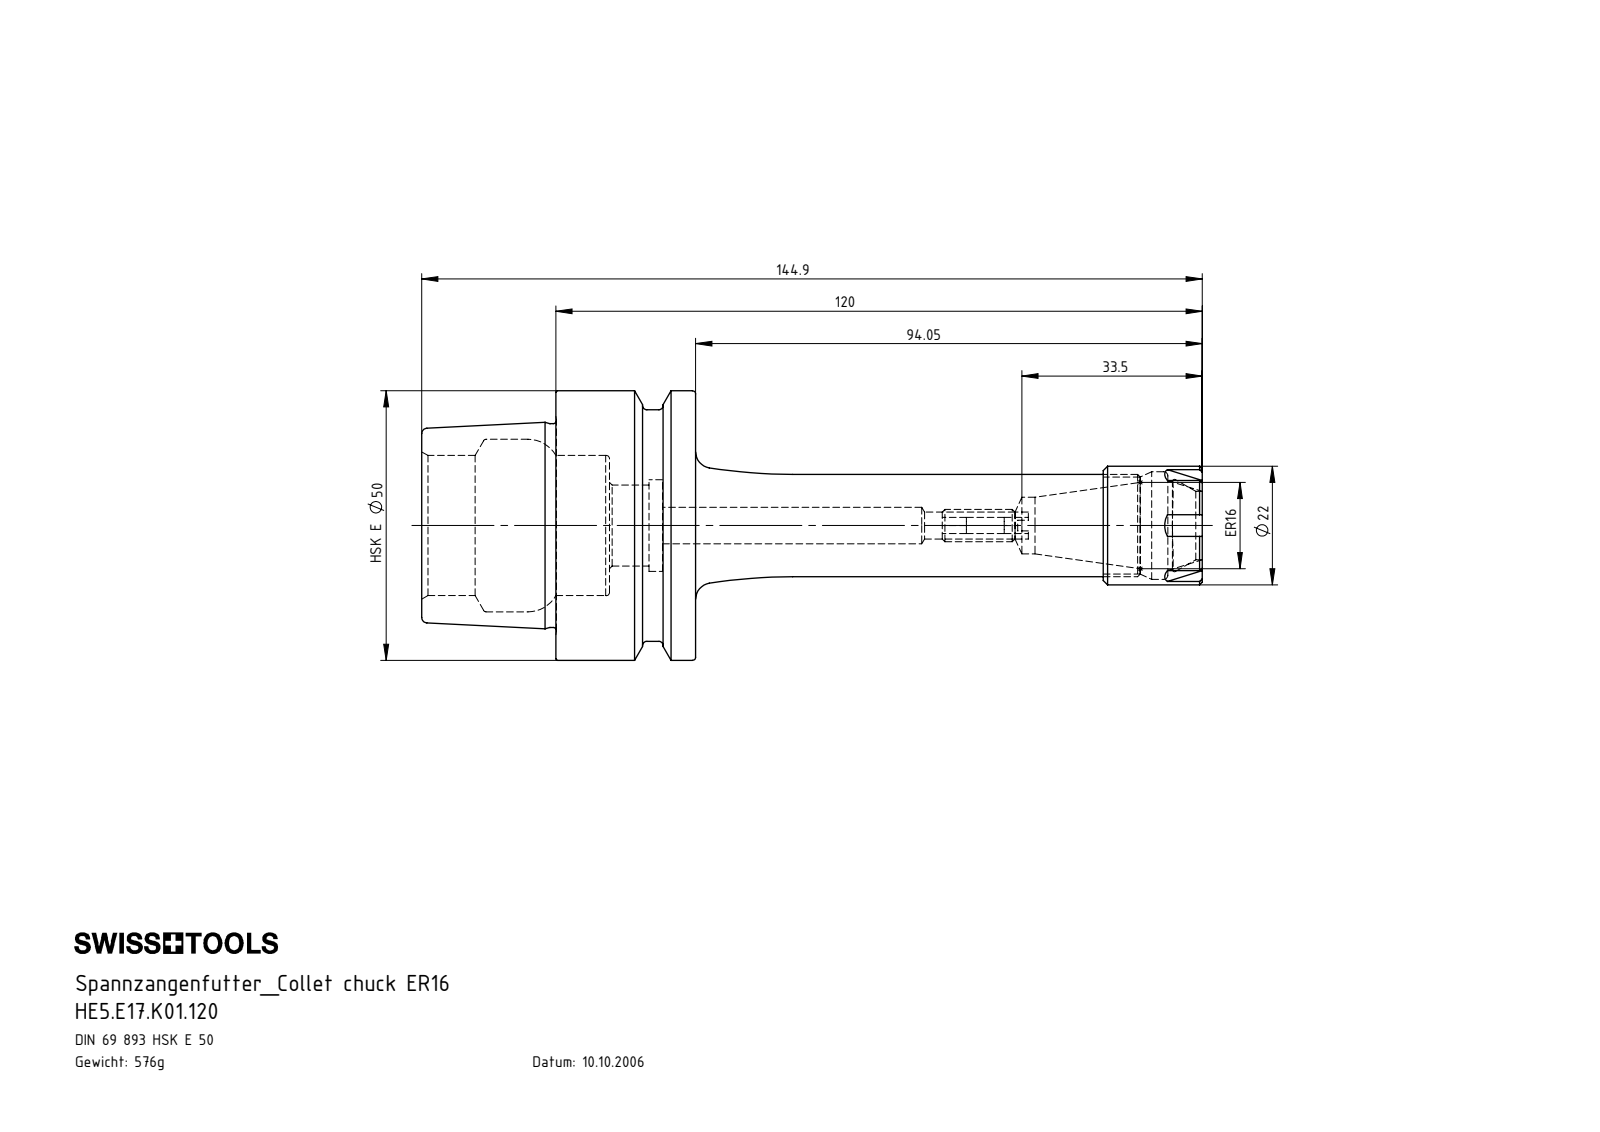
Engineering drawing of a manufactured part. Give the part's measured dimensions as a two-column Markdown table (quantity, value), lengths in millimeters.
| quantity | value |
| --- | --- |
| part name | E17-ER1.001.018; HE5-E17.K01.120_A_Fertigbearbeitung; ERU-AN2.K01.016_A; HE5.E17.K01.120 |
| STEP written by | SolidWorks 2017 (CONFIG_CONTROL_DESIGN) |
| units | millimeters |
| bodies | 3 solids, 185 faces (66 planar, 43 cylindrical, 76 other) |
| overall size | 144.9 × 50 × 50 |
| volume | 73 353 mm³ |
| surface area | 25 163 mm² |
| round holes (diameter × count) | 3 × 1, 5 × 1, 6.8 × 1, 10.5 × 1, 12.7 × 1, 15 × 1, 17 × 1, 18 × 1, 20 × 1, 26 × 1, 32 × 1 |
| round bosses / shafts (diameter × count) | 50 × 1, 42.95 × 1, 37.81 × 1, 22 × 1, 19 × 1, 6 × 1 |
| partial cylindrical surfaces (radius × count) | 7.7 × 2 |
| main face-to-face distances | 25.95, 24.9, 50.85, 16, 34.85, 9.95, 44.7, 19.8, 9.85, 6.15 |
